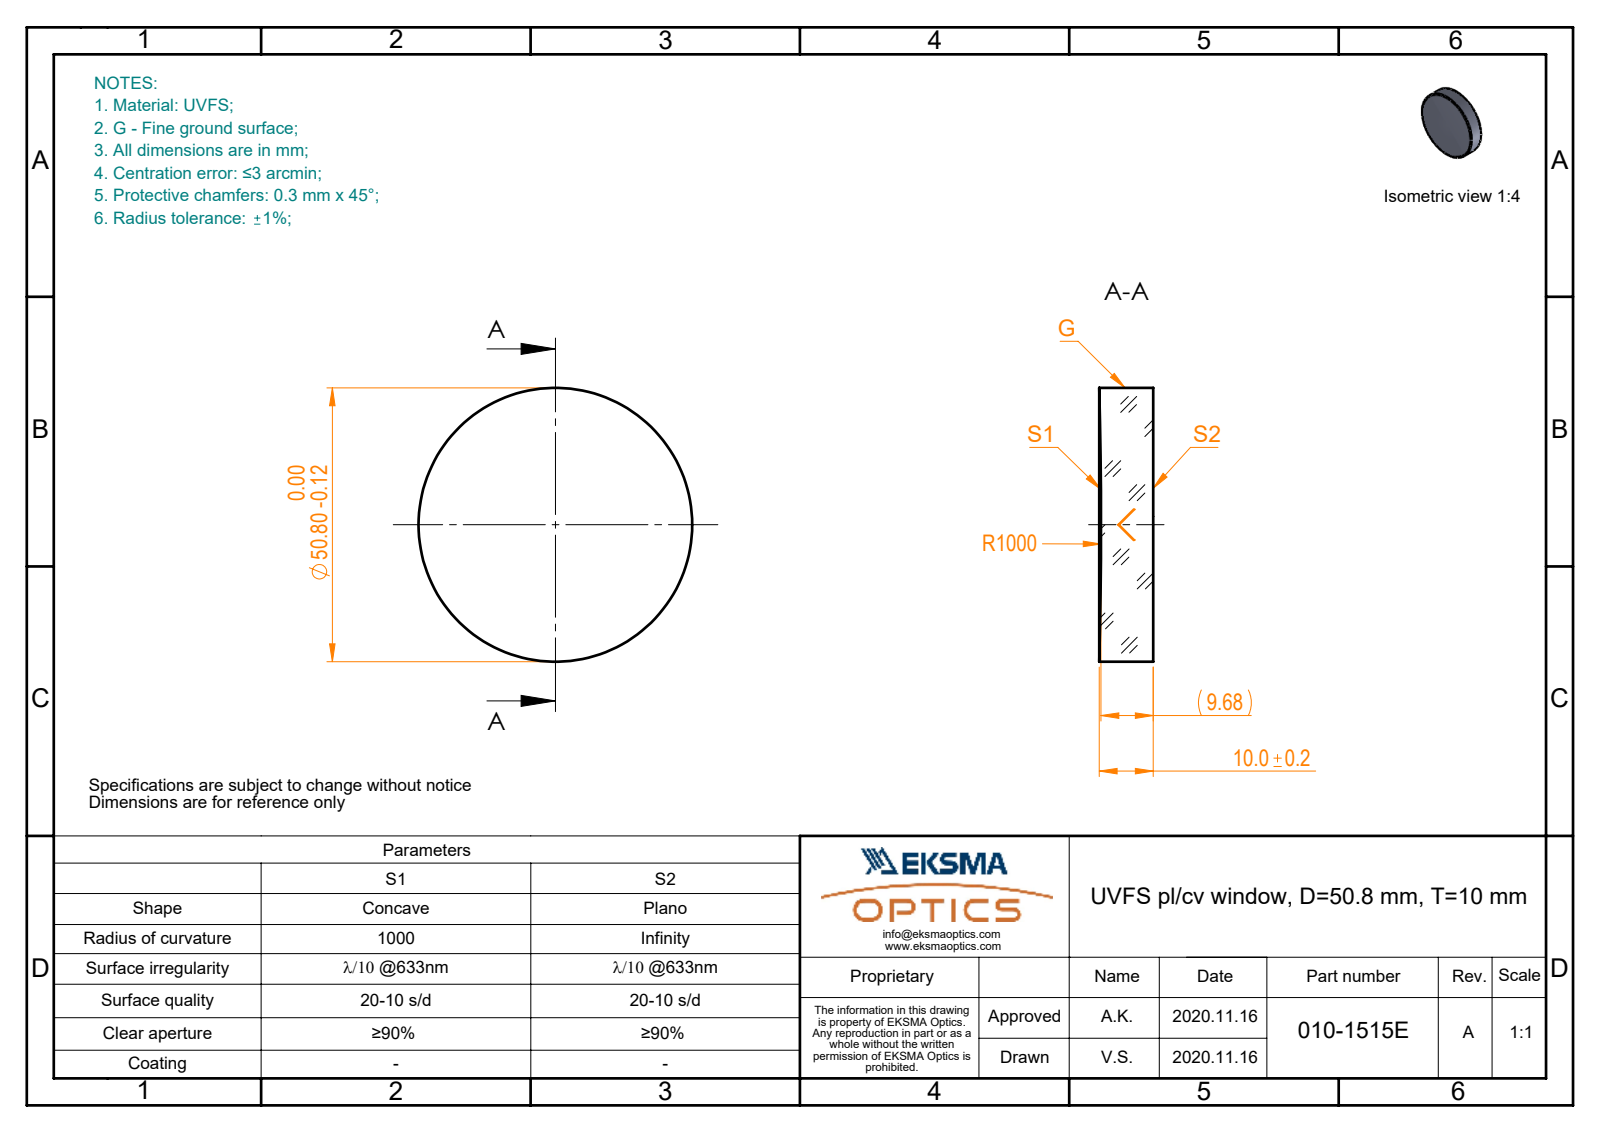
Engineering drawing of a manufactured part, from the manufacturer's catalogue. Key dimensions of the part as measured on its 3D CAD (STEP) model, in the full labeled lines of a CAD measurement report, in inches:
Part name (STEP PRODUCT): 010-1515E_UVFS_PCV_window
STEP written by: SolidWorks 2019 (CONFIG_CONTROL_DESIGN)
Units: inches
Bodies: 1 solid, 5 faces (1 planar, 2 cylindrical, 2 other)
Overall size (bounding box): 2 × 2 × 0.394
Volume: 1.217 in³ · Surface area: 8.758 in²
Round bosses / shafts (diameter × count): ⌀2 ×1
